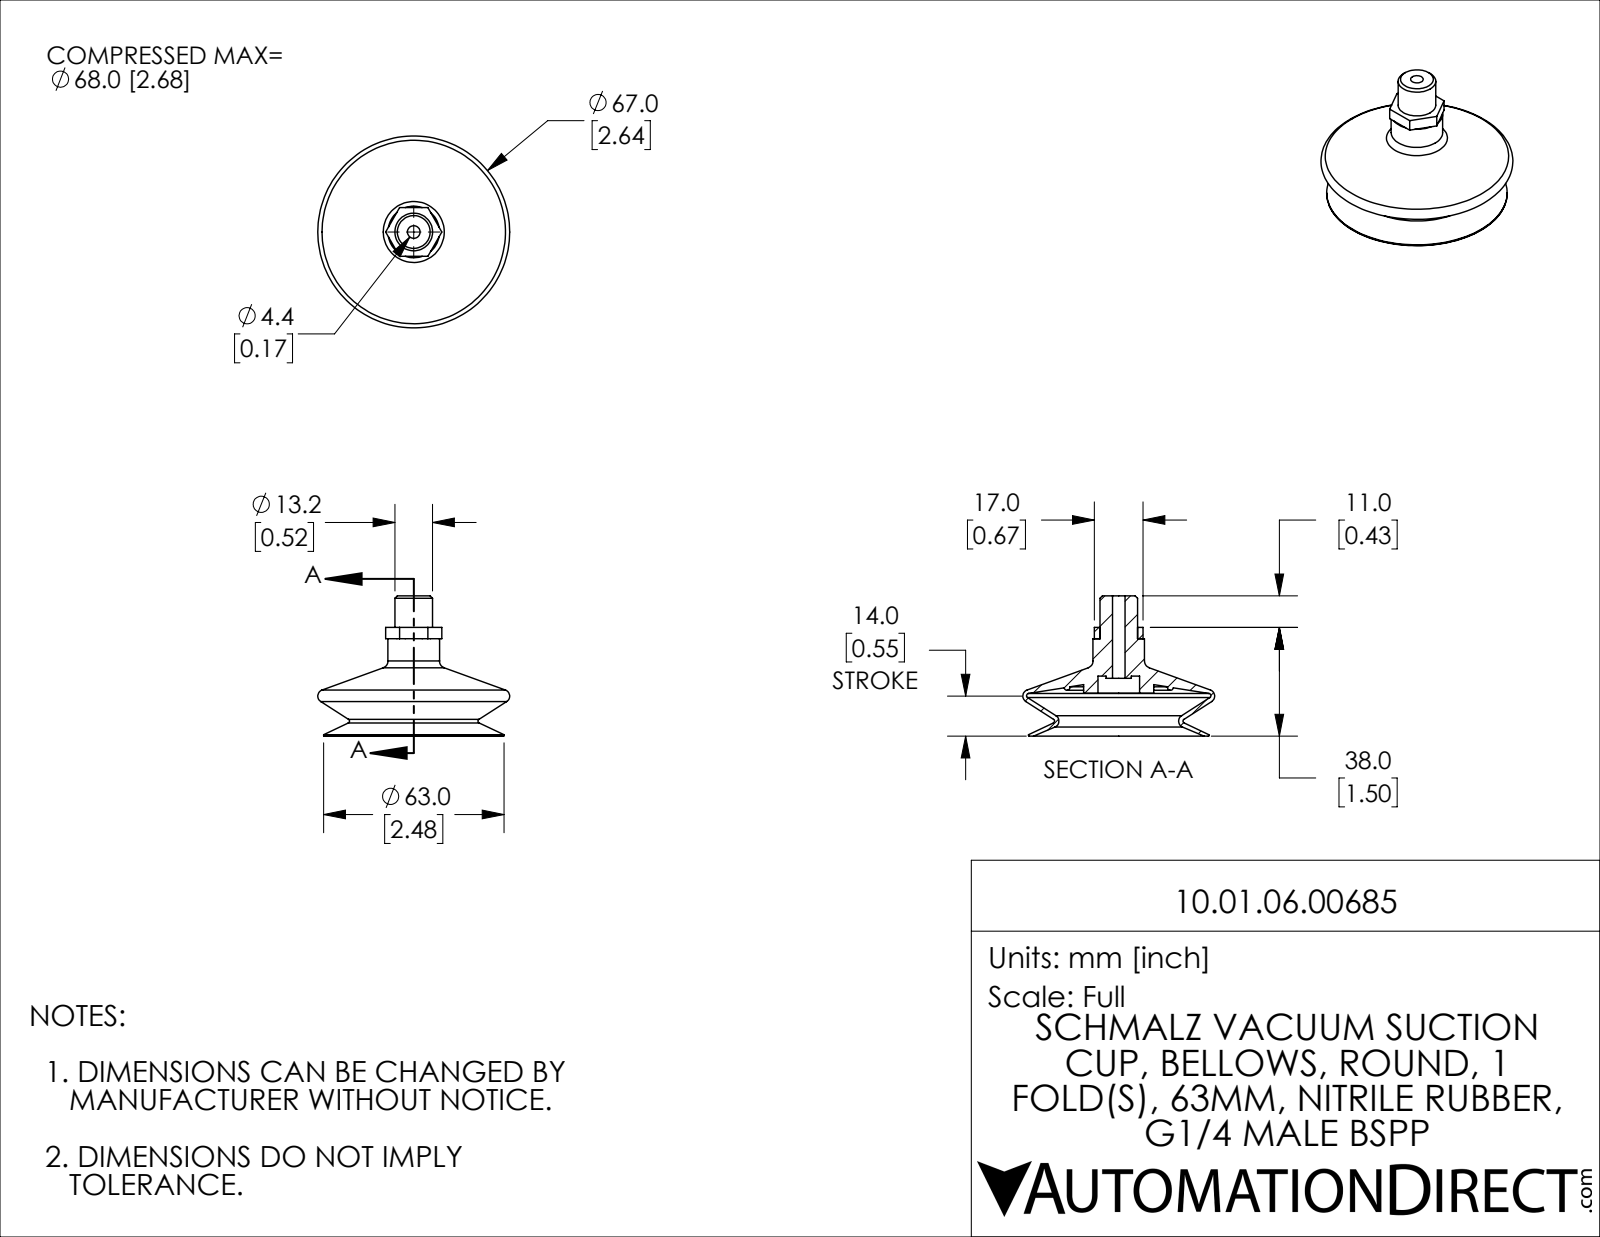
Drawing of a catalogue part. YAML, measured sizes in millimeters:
part_name: "10.01.06.00685"
step_written_by: "SolidWorks 2021 (CONFIG_CONTROL_DESIGN)"
units: millimeters
bodies: {solids: 2, faces: 68, planar: 14, cylindrical: 14, other: 40}
overall_size: [67, 67, 49]
volume: 22958
surface_area: 18999
round_holes:
  - {diameter: 4.4, count: 1}
  - {diameter: 13.16, count: 1}
  - {diameter: 14.5, count: 1}
round_bosses_or_shafts:
  - {diameter: 63, count: 1}
  - {diameter: 24.5, count: 1}
  - {diameter: 8.8, count: 1}
face_to_face_distances: [15, 34, 19, 17, 38, 23, 4, 21, 6, 13]
